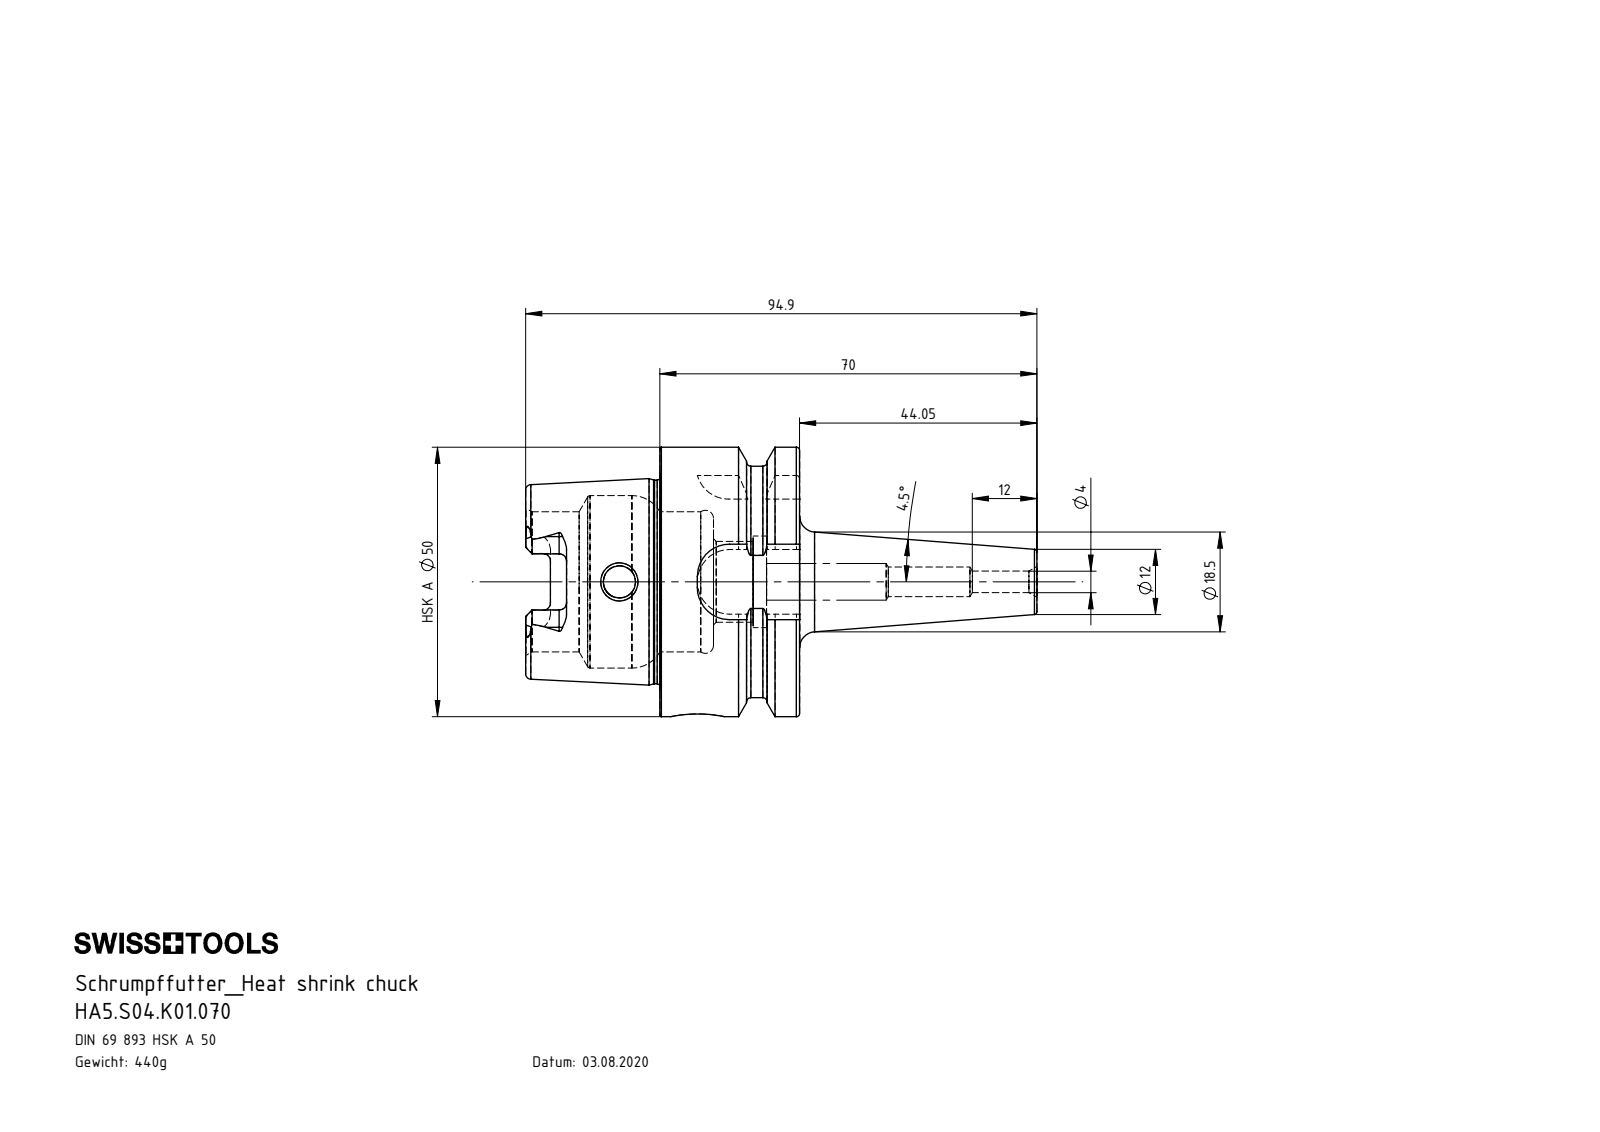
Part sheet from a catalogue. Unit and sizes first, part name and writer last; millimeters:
Units: millimetres
Overall size (bounding box): 94.9 × 50 × 50
Round holes (diameter × count): ⌀4 ×1, ⌀5.5 ×1, ⌀6 ×1, ⌀6.8 ×1, ⌀10 ×1, ⌀15 ×1, ⌀17 ×1, ⌀26 ×1, ⌀32 ×1
Round bosses / shafts (diameter × count): ⌀50 ×1, ⌀42.95 ×1, ⌀37.81 ×1
Partial cylindrical surfaces — rounded edges, fillets, slot ends (radius × count): R1.4 ×6, R2.38 ×4, R6 ×4
Main face-to-face distances: 25.95, 9.95, 16, 24.9, 34.85, 50.85, 41.8, 44.7, 19.8, 9.85
Volume: 56 097 mm³ · Surface area: 17 819 mm²
Bodies: 1 solid, 162 faces (46 planar, 47 cylindrical, 69 other)
Part name (STEP PRODUCT): HA5.S04.K01.070; HA5-S04.K01.070_A_Fertigbearbeitung
STEP written by: SolidWorks 2022 (AUTOMOTIVE_DESIGN)
